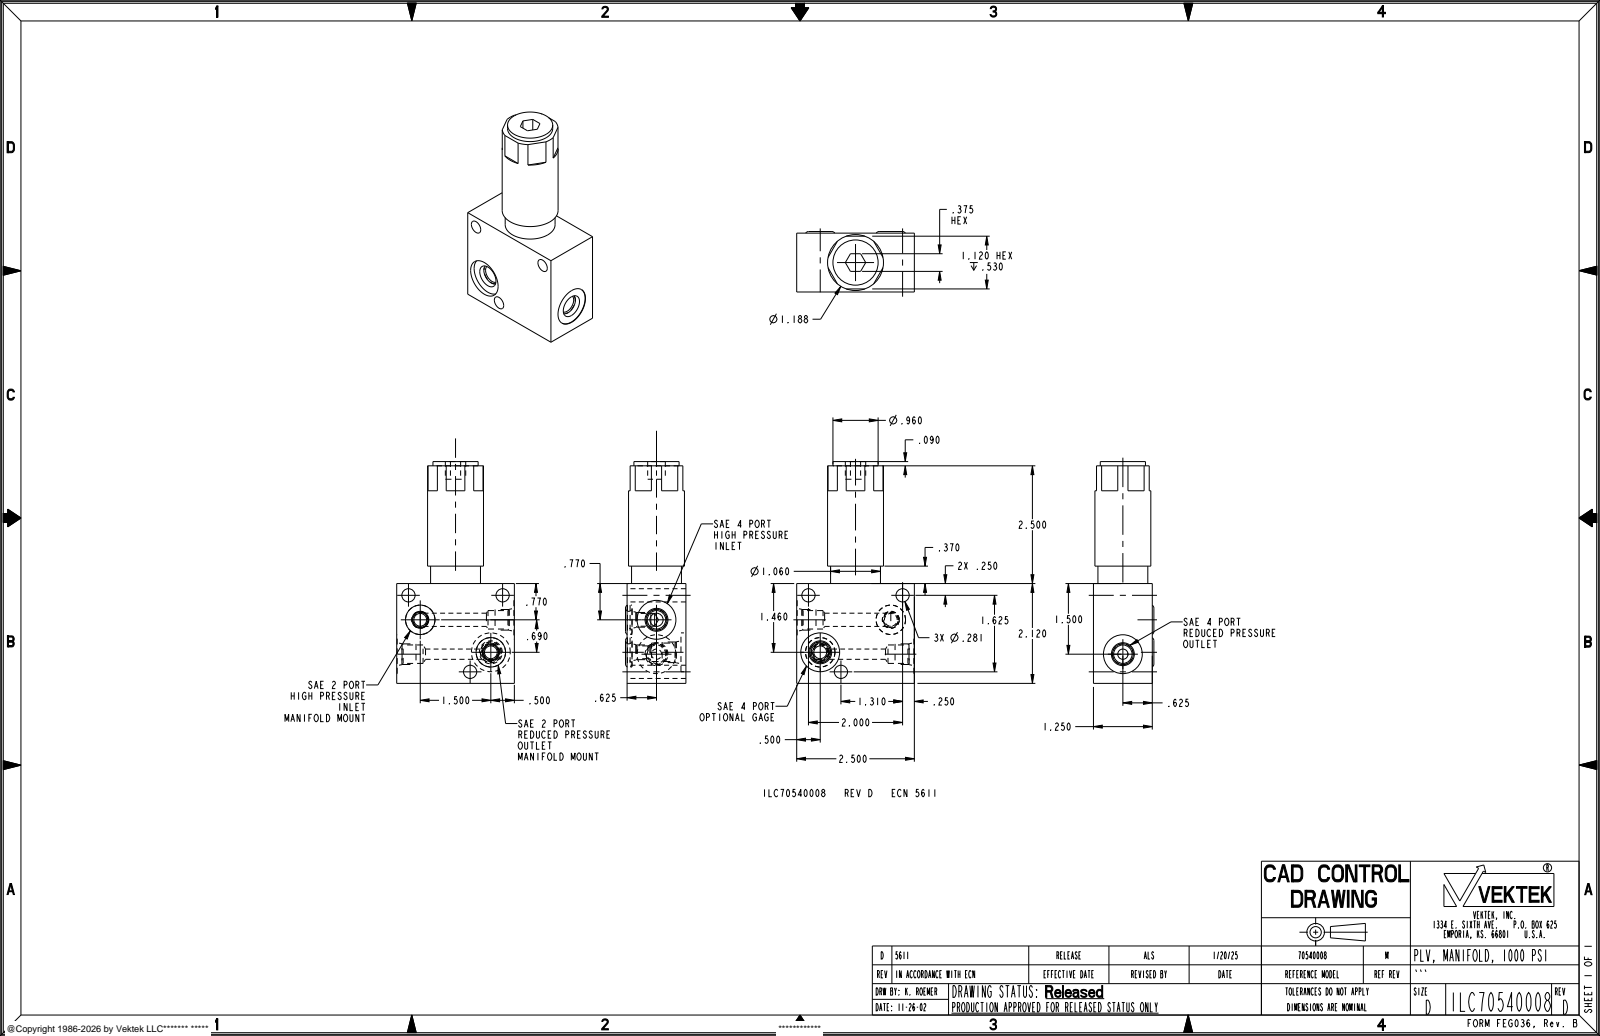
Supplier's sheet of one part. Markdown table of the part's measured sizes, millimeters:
| quantity | value |
| --- | --- |
| part name | ILC70540008 |
| STEP written by | CREO PARAMETRIC BY PTC INC, 2021164 (AUTOMOTIVE_DESIGN) |
| units | millimeters |
| bodies | 1 solid, 120 faces (39 planar, 50 cylindrical, 31 other) |
| overall size | 119.6 × 63.5 × 32.6 |
| volume | 140 400 mm³ |
| surface area | 28 150 mm² |
| round holes (diameter × count) | 7.1 × 4, 10 × 3, 21 × 3, 6.9 × 2, 15.9 × 2, 5.5 × 1 |
| round bosses / shafts (diameter × count) | 11.1 × 3, 7.9 × 2, 30.2 × 1, 26.9 × 1, 24.4 × 1 |
| main face-to-face distances | 31.8, 63.5, 53.8, 63.2, 2.7, 29.1, 28.4, 119.6, 65.8, 9.4 |
| hole center spacings | 14.7, 15.4, 18.5, 31.4, 38.9, 41.9, 44.9, 46.4 |
